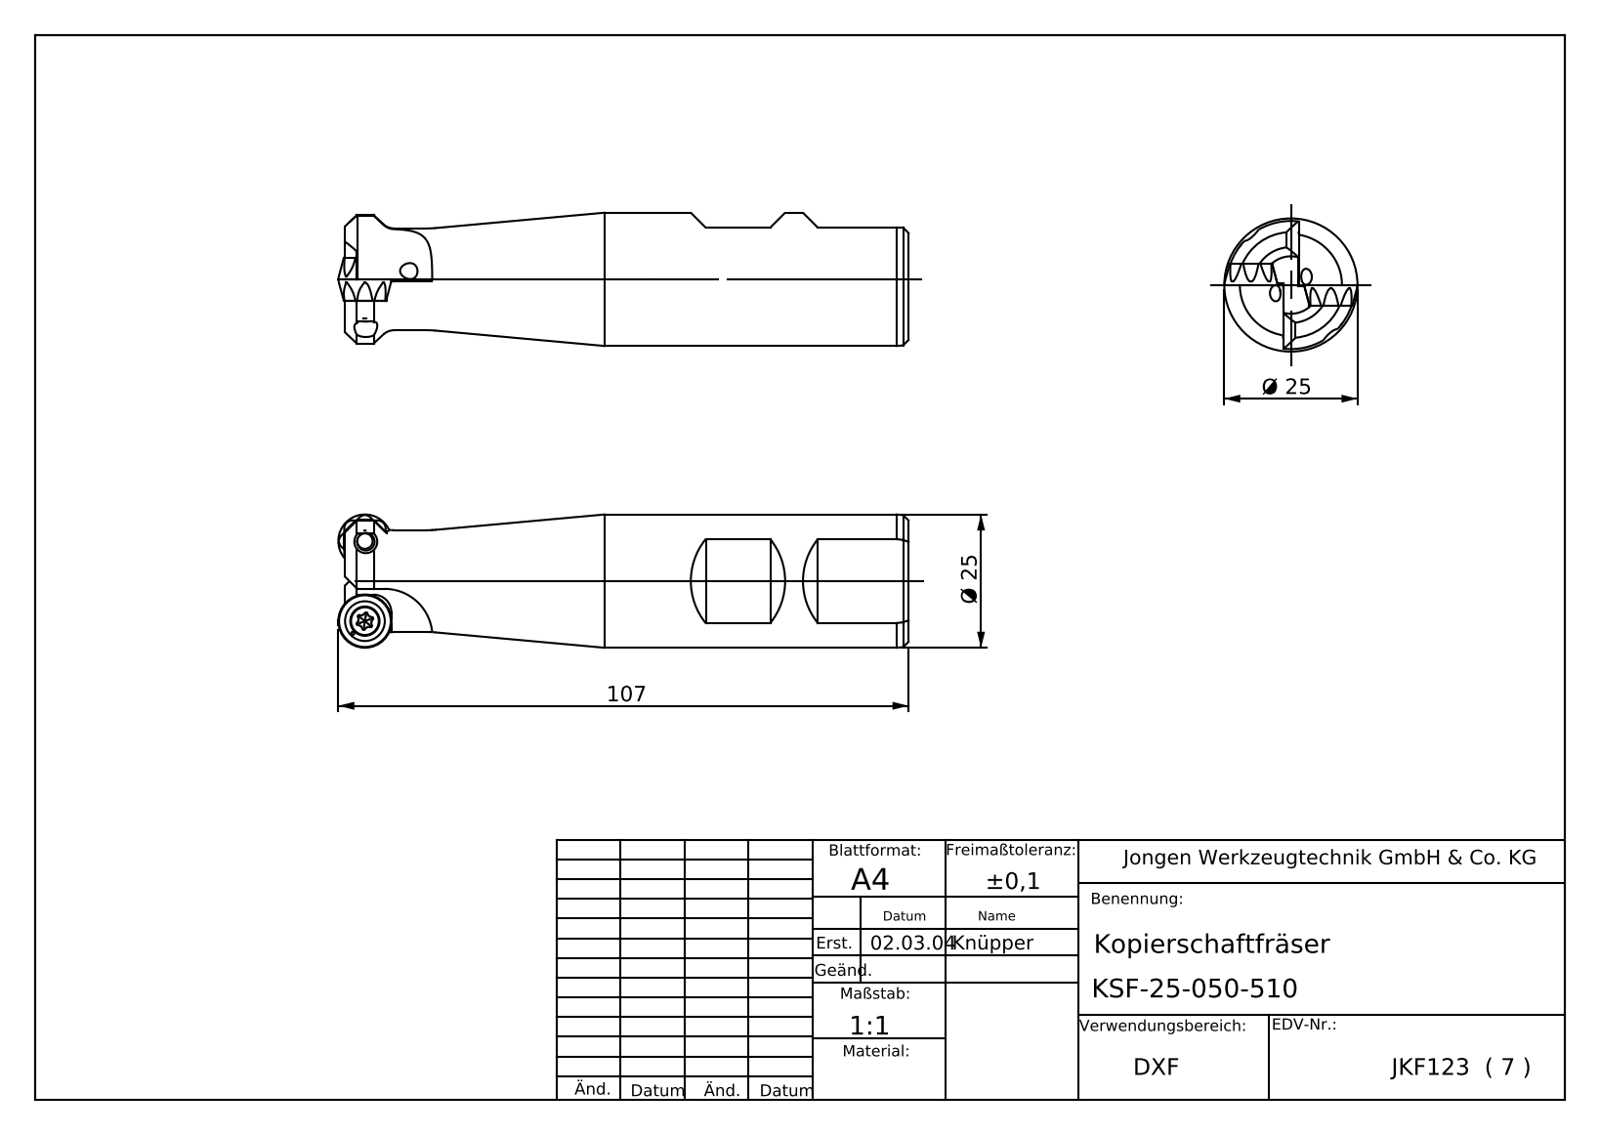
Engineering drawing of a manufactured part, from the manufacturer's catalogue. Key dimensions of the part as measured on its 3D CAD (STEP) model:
Part name (STEP PRODUCT): KSF-25-050-510
STEP written by: SolidWorks 2013 (AUTOMOTIVE_DESIGN)
Units: millimetres
Bodies: 1 solid, 50 faces (25 planar, 11 cylindrical, 14 other)
Overall size (bounding box): 107.02 × 25.02 × 25.02
Volume: 42 517 mm³ · Surface area: 10 760 mm²
Round holes (diameter × count): ⌀3 ×2, ⌀2 ×1, ⌀4 ×1, ⌀6.5 ×1
Round bosses / shafts (diameter × count): ⌀25 ×1
Partial cylindrical surfaces — rounded edges, fillets, slot ends (radius × count): R9 ×2, R9.55 ×1
Main face-to-face distances: 9.4, 0.6, 10, 14.88, 103.55, 11.31, 26.19, 2.92, 4.78
